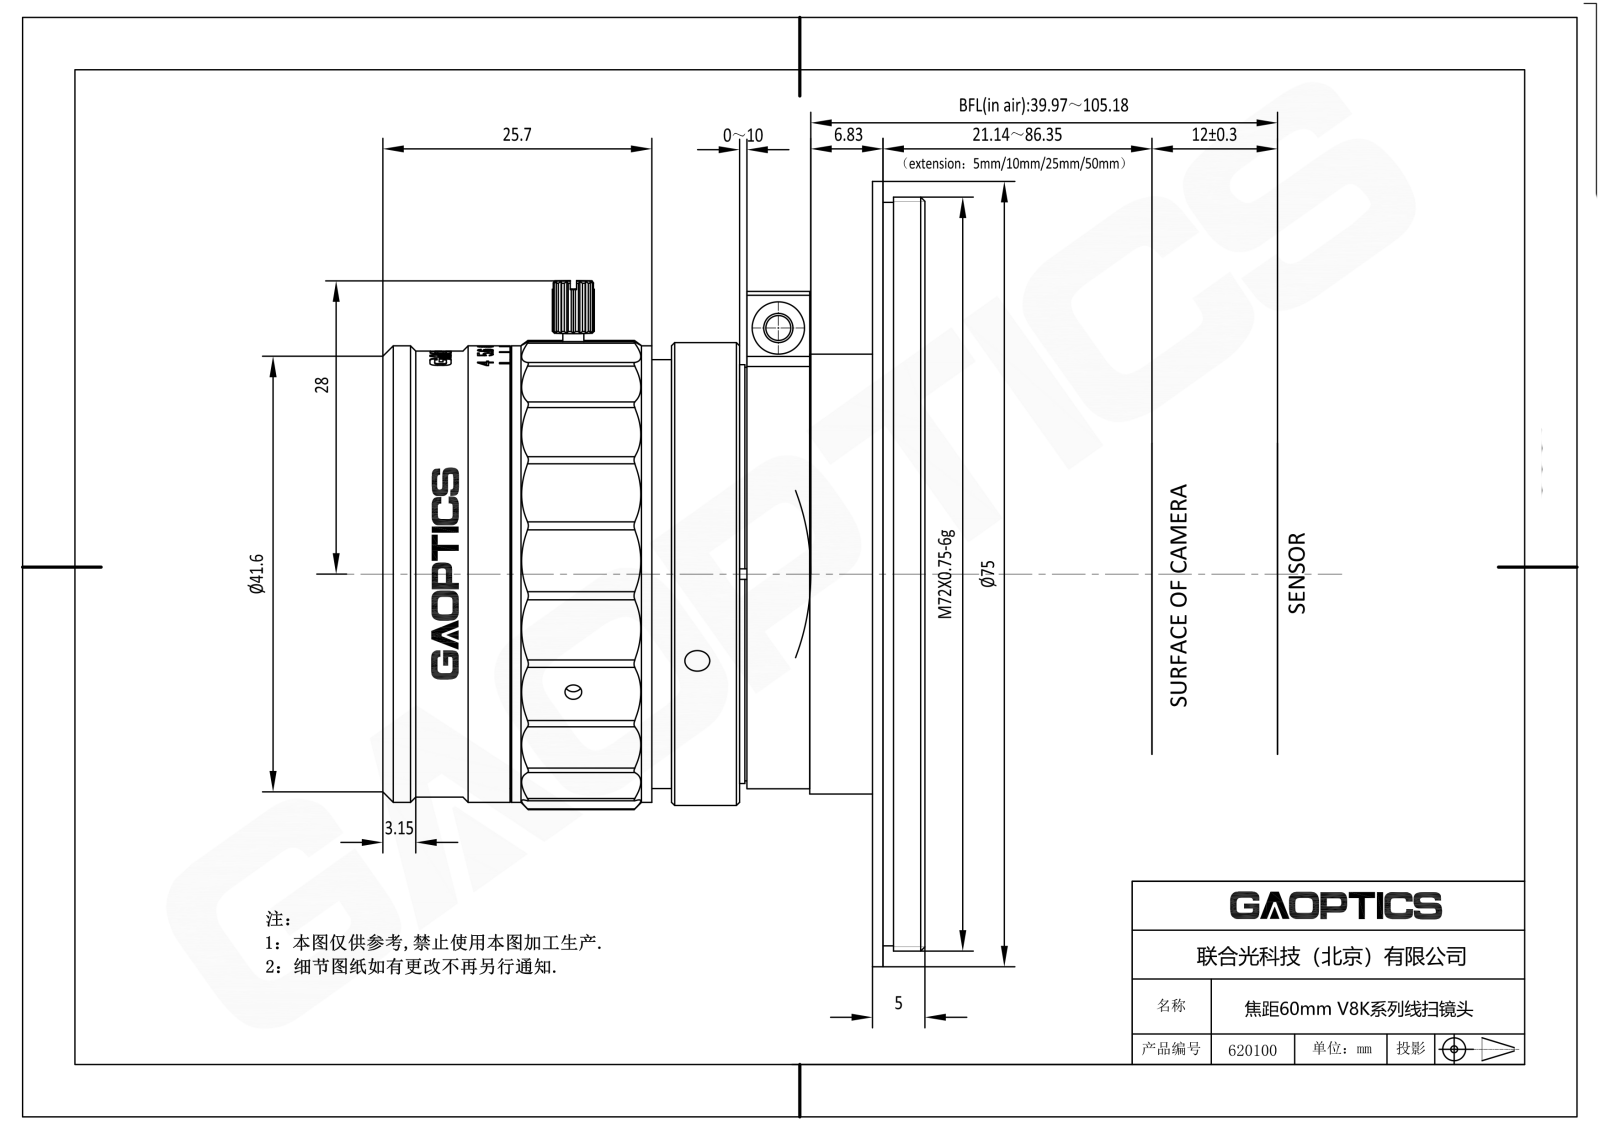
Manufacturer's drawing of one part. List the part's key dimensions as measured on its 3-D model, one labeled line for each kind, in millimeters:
Part name (STEP PRODUCT): 620100
STEP written by: SolidWorks 2019 (CONFIG_CONTROL_DESIGN)
Units: millimetres
Bodies: 8 solids, 1491 faces (501 planar, 264 cylindrical, 726 other)
Overall size (bounding box): 75 × 75 × 51.78
Volume: 54 506 mm³ · Surface area: 38 093 mm²
Round holes (diameter × count): ⌀1.6 ×3, ⌀2.6 ×3, ⌀2.4 ×1, ⌀3.2 ×1, ⌀5 ×1, ⌀18.63 ×1, ⌀19.02 ×1, ⌀19.4 ×1, ⌀19.8 ×1, ⌀20.2 ×1, ⌀20.6 ×1, ⌀21 ×1
Round bosses / shafts (diameter × count): ⌀75 ×1, ⌀72 ×1, ⌀71 ×1, ⌀44.2 ×1, ⌀43.6 ×1, ⌀42.6 ×1, ⌀42 ×1, ⌀41 ×1
Partial cylindrical surfaces — rounded edges, fillets, slot ends (radius × count): R1 ×23, R12 ×21, R2 ×1, R12.05 ×1, R21.25 ×1, R21.75 ×1, R27 ×1
Main face-to-face distances: 1, 5, 4, 19.2, 2, 43.78, 7, 6, 14.7, 15.7
